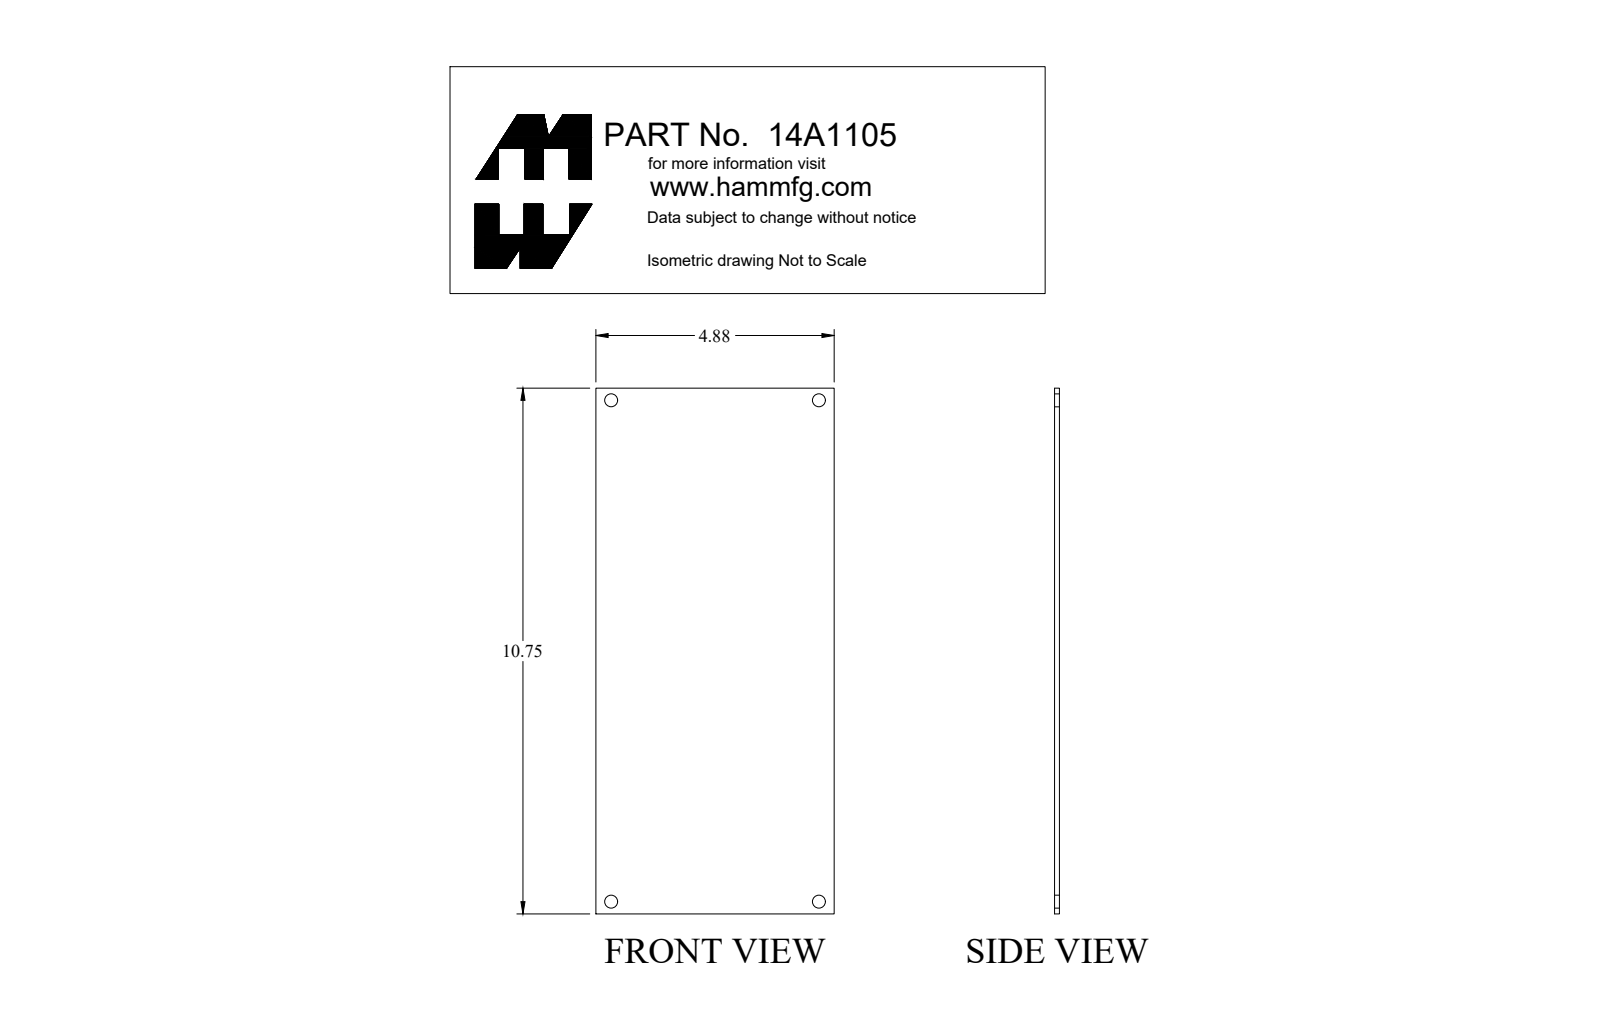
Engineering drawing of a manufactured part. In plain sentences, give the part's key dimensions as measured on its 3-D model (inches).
The part is named "14A1105". Its 3-D file was written by "SolidWorks 2018 (AUTOMOTIVE_DESIGN)". It is 1 solid with 10 faces: 6 planar, 4 cylindrical and 0 other. Overall it measures 10.75 by 4.875 by 0.1 inches. Its volume is 5.219 cubic inches and its surface area 107.8 square inches. Round holes: 4 of diameter 0.265. The main face-to-face distances are 0.1, 4.875, 10.75. The hole center spacings are 4.251, 10.25, 11.096.
